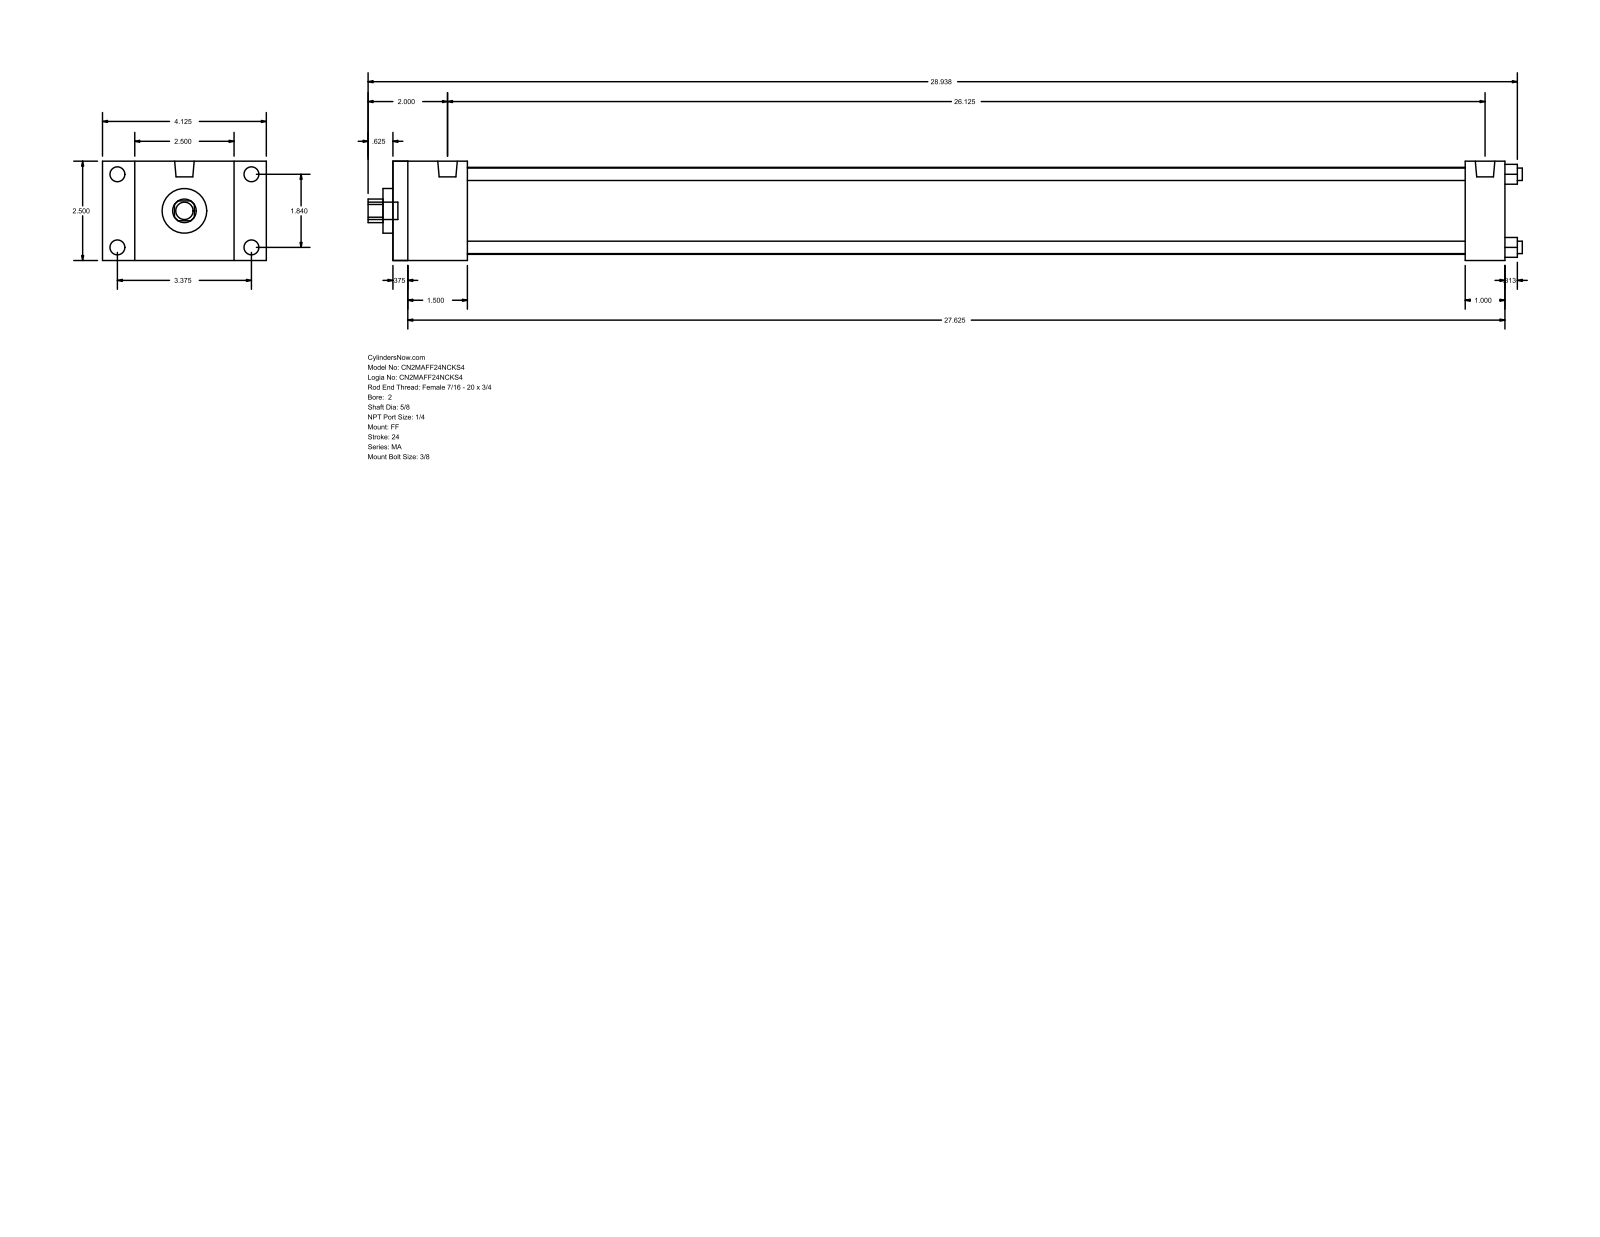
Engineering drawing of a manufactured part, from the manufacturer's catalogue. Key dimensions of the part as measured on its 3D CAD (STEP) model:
Part name (STEP PRODUCT): MA_FF__0200_0.625
STEP written by: GSSL Pune (CONFIG_CONTROL_DESIGN)
Units: millimetres
Bodies: 0 solids, 92 faces (64 planar, 28 cylindrical, 0 other)
Overall size (bounding box): 738.19 × 104.78 × 63.5
Round holes (diameter × count): ⌀7.94 ×4, ⌀15.88 ×1, ⌀28.57 ×1, ⌀55.63 ×1
Round bosses / shafts (diameter × count): ⌀9.53 ×4, ⌀7.94 ×4, ⌀12.49 ×2, ⌀11.11 ×1
Partial cylindrical surfaces — rounded edges, fillets, slot ends (radius × count): R7.54 ×1
Main face-to-face distances: 63.5, 711.2, 9.52, 701.68, 38.1, 47.62, 685.79, 676.27, 638.17, 663.58
Hole centre spacings: 33.05, 46.74, 66.1
